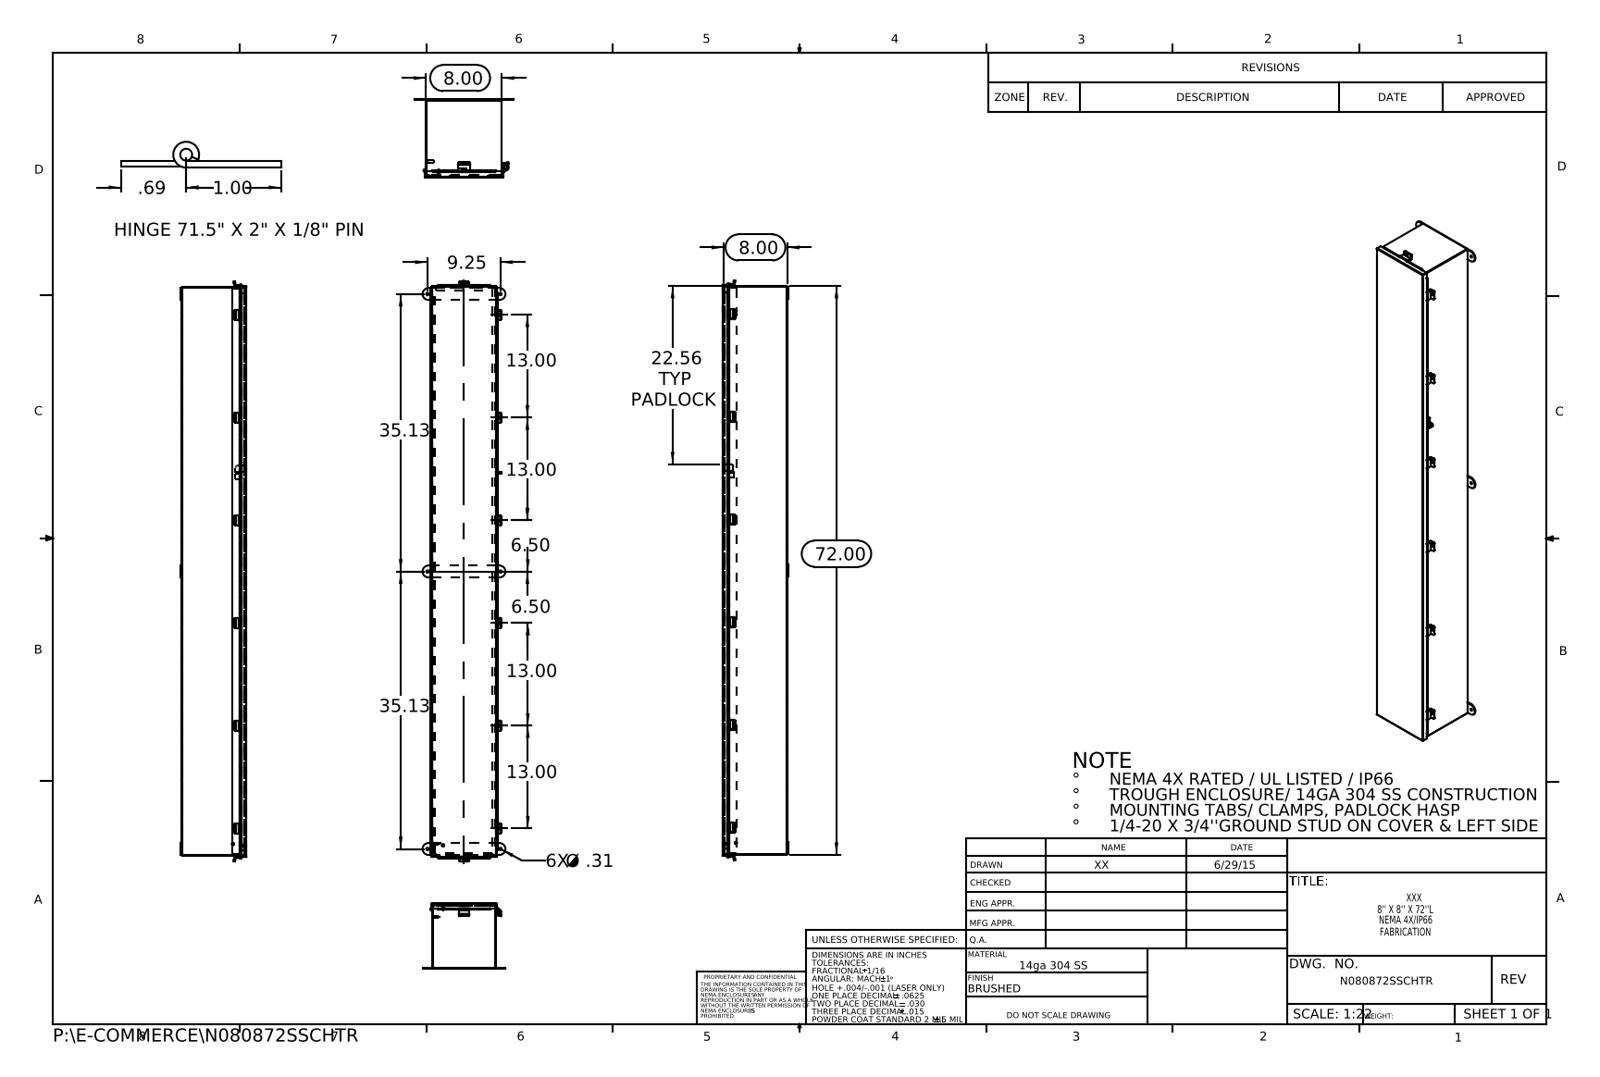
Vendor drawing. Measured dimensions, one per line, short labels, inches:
name: N080872SSCHTR; N080872SSCHTR JIC Mounting Bracket; N080872SSCHTR JIC_Cover_Template; HW-CLH-JH-20104 (+8 more)
written by: SolidWorks 2015 (CONFIG_CONTROL_DESIGN)
unit: in
bodies: 29 solids, 1917 faces (1137 planar, 760 cylindrical, 20 other)
size: 73.407 × 10.5 × 8.337
volume: 211.7 in³; area: 5 692 in²
holes: 8× ⌀0.25, 6× ⌀0.313, 1× ⌀0.125, 1× ⌀0.375, 1× ⌀0.375
bosses: 2× ⌀0.315, 2× ⌀0.236, 1× ⌀0.273, 1× ⌀0.25
rounds: 31× R0.125, 16× R0.133, 12× R0.009, 12× R0.013, 11× R0.088, 6× R0.083, 6× R0.1, 6× R0.75
face distances: 0.075, 7.925, 8.128, 8, 7.85, 8.203, 8.053, 0.149, 8.074, 0.074
hole spacings: 13, 26, 35.125, 36.323, 39, 9.25, 52, 70.25
